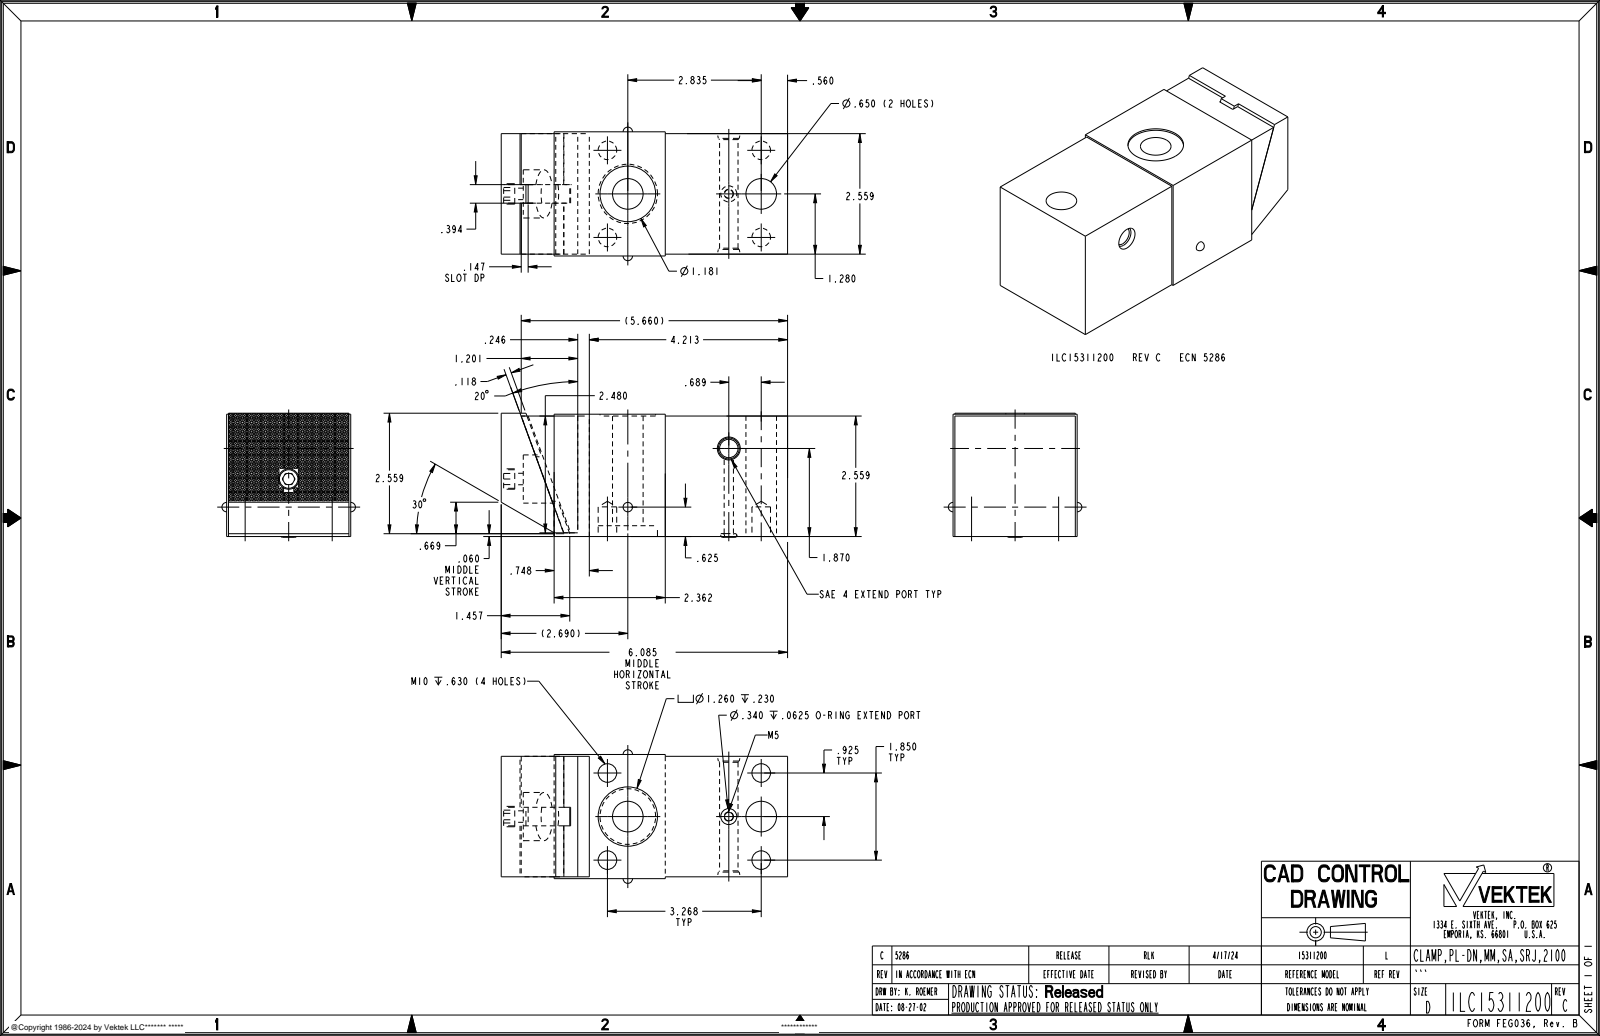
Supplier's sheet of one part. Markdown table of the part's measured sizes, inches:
| quantity | value |
| --- | --- |
| part name | ILC15311200 |
| STEP written by | CREO PARAMETRIC BY PTC INC, 2021164 (AUTOMOTIVE_DESIGN) |
| units | inches |
| bodies | 2 solids, 116 faces (62 planar, 30 cylindrical, 24 other) |
| overall size | 6.085 × 2.837 × 2.636 |
| volume | 34.63 in³ |
| surface area | 122.1 in² |
| round holes (diameter × count) | 0.394 × 4, 0.65 × 2, 0.197 × 1, 0.244 × 1, 0.34 × 1, 0.392 × 1, 0.433 × 1, 1.024 × 1, 1.181 × 1, 1.26 × 1 |
| round bosses / shafts (diameter × count) | 0.394 × 1 |
| main face-to-face distances | 2.559, 2.598, 0.039, 4.213, 0.246, 4.459, 2.637, 1.626, 1.872, 6.085 |
| hole center spacings | 0.925, 1.022, 1.154, 1.85, 2.74, 2.982, 3.268, 3.396 |
